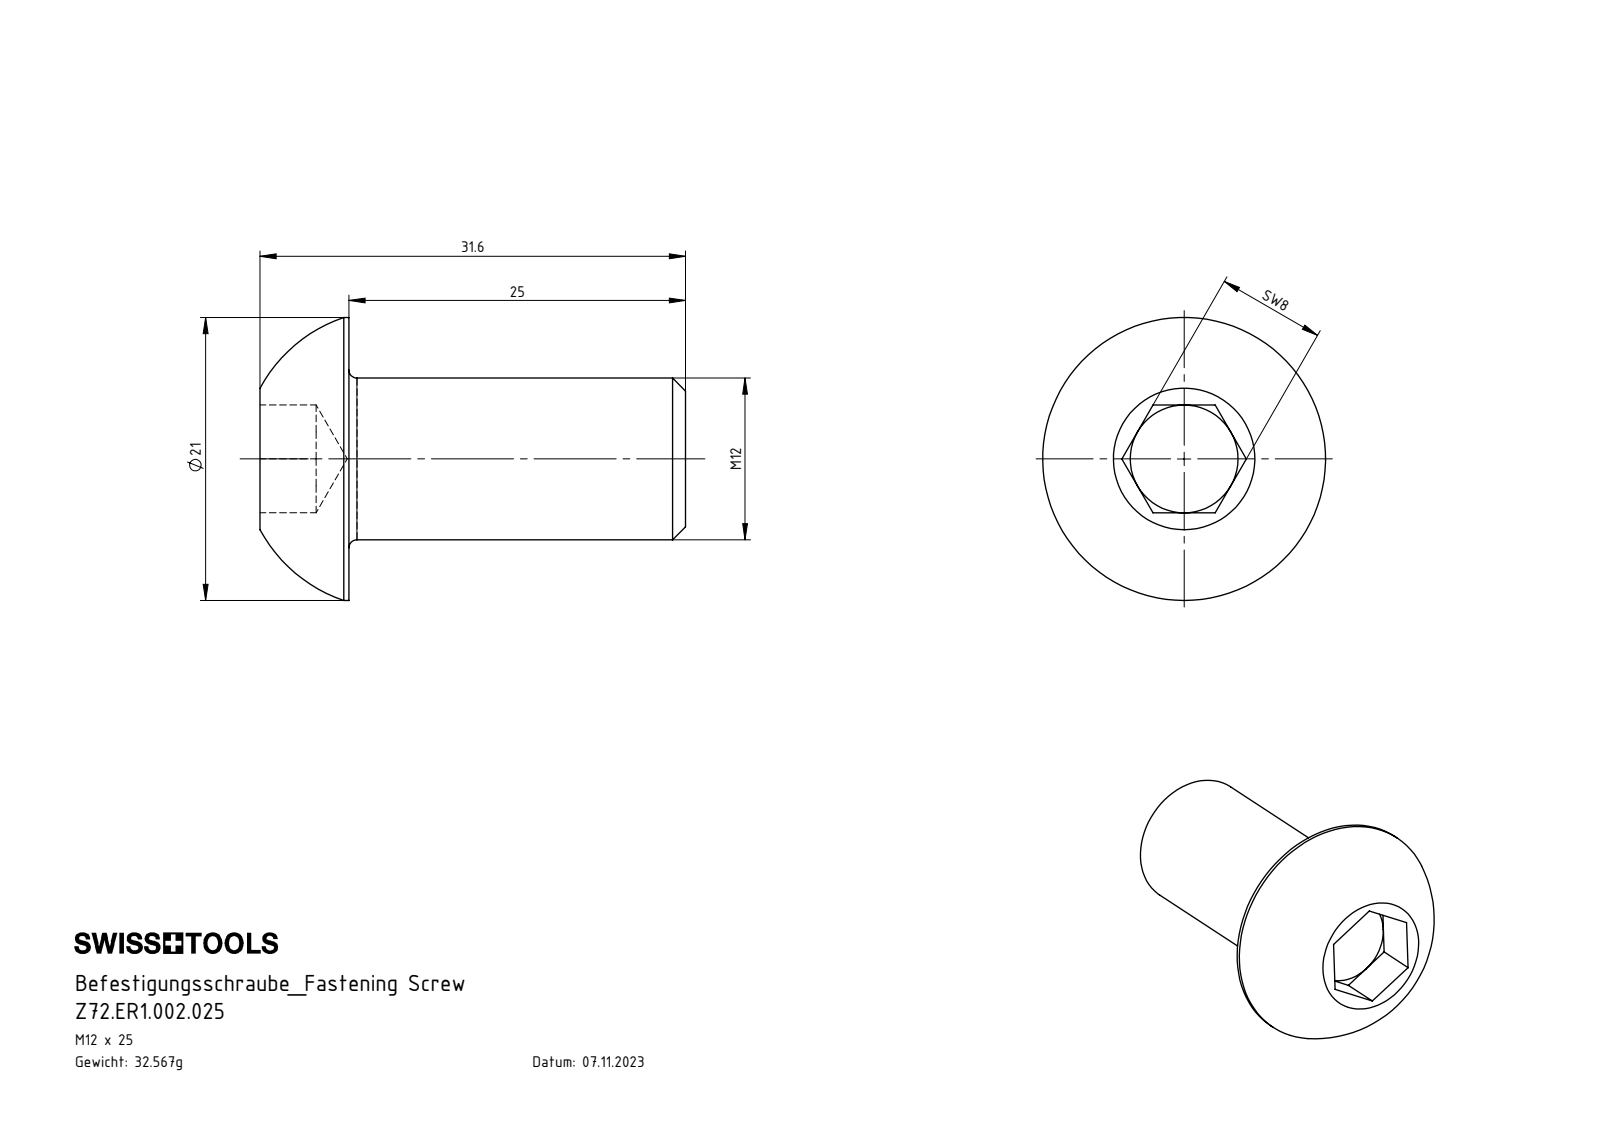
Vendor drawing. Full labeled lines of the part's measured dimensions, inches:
Part name (STEP PRODUCT): Z72.ER1.002.025
STEP written by: SolidWorks 2017 (AUTOMOTIVE_DESIGN)
Units: inches
Bodies: 1 solid, 27 faces (15 planar, 4 cylindrical, 8 other)
Overall size (bounding box): 1.244 × 0.827 × 0.827
Volume: 0.253 in³ · Surface area: 2.984 in²
Round bosses / shafts (diameter × count): ⌀0.827 ×1, ⌀0.472 ×1
Main face-to-face distances: 0.984, 0.315, 0.26, 1.244, 0.164, 0.096, 1.08
